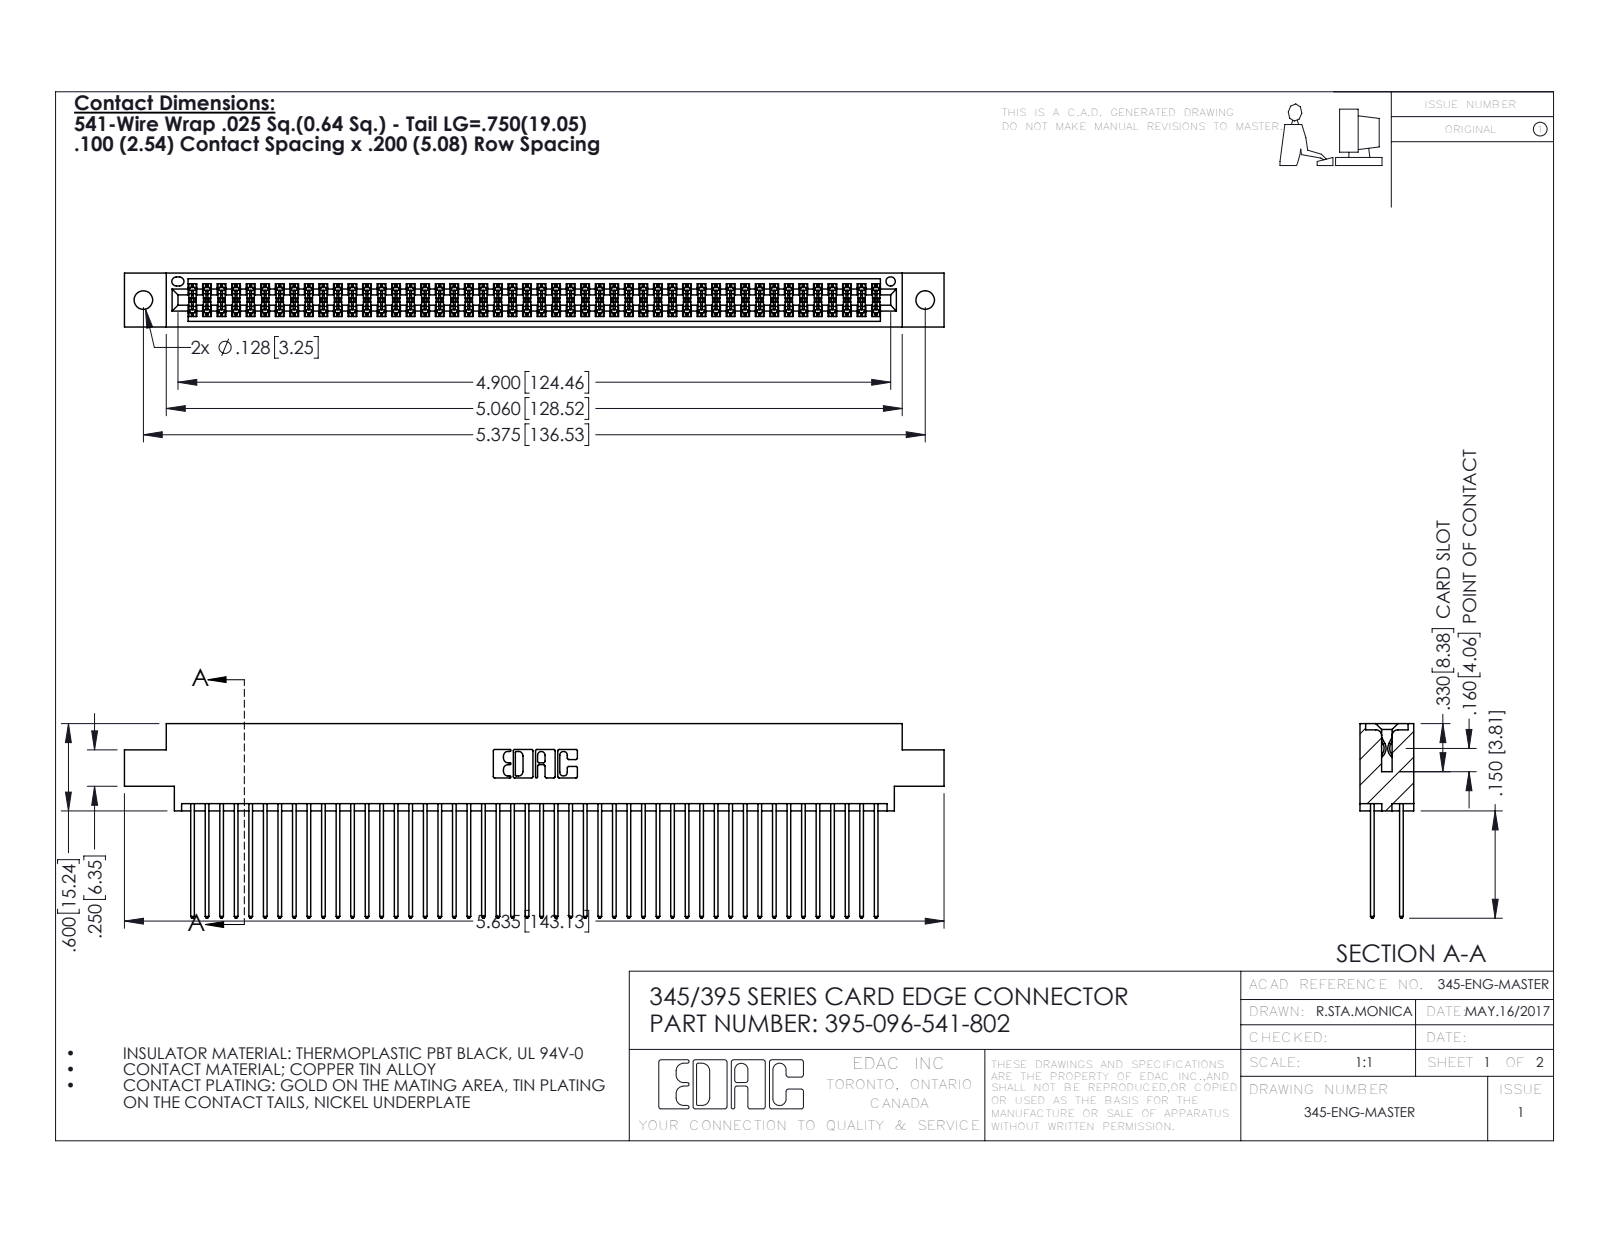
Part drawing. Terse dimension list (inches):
name: 395-096-541-802; 345-292-001_345-293-141; 345 Part_0.170 Offset - 0.128 Dia
written by: SolidWorks 2016 (CONFIG_CONTROL_DESIGN)
unit: in
bodies: 97 solids, 4930 faces (3252 planar, 1678 cylindrical, 0 other)
size: 5.635 × 1.337 × 0.37
volume: 0.876 in³; area: 36.89 in²
holes: 2× ⌀0.128, 1× ⌀0.064
rounds: 144× R0.006, 96× R0.01, 22× R0.01, 6× R0.007, 6× R0.031, 3× R0.026, 2× R0.014, 2× R0.019
face distances: 0.072, 0.298, 0.2, 0.098, 0.272, 0.025, 0.37, 0.225, 0.175, 0.149
hole spacings: 0.27, 5.139, 5.375
